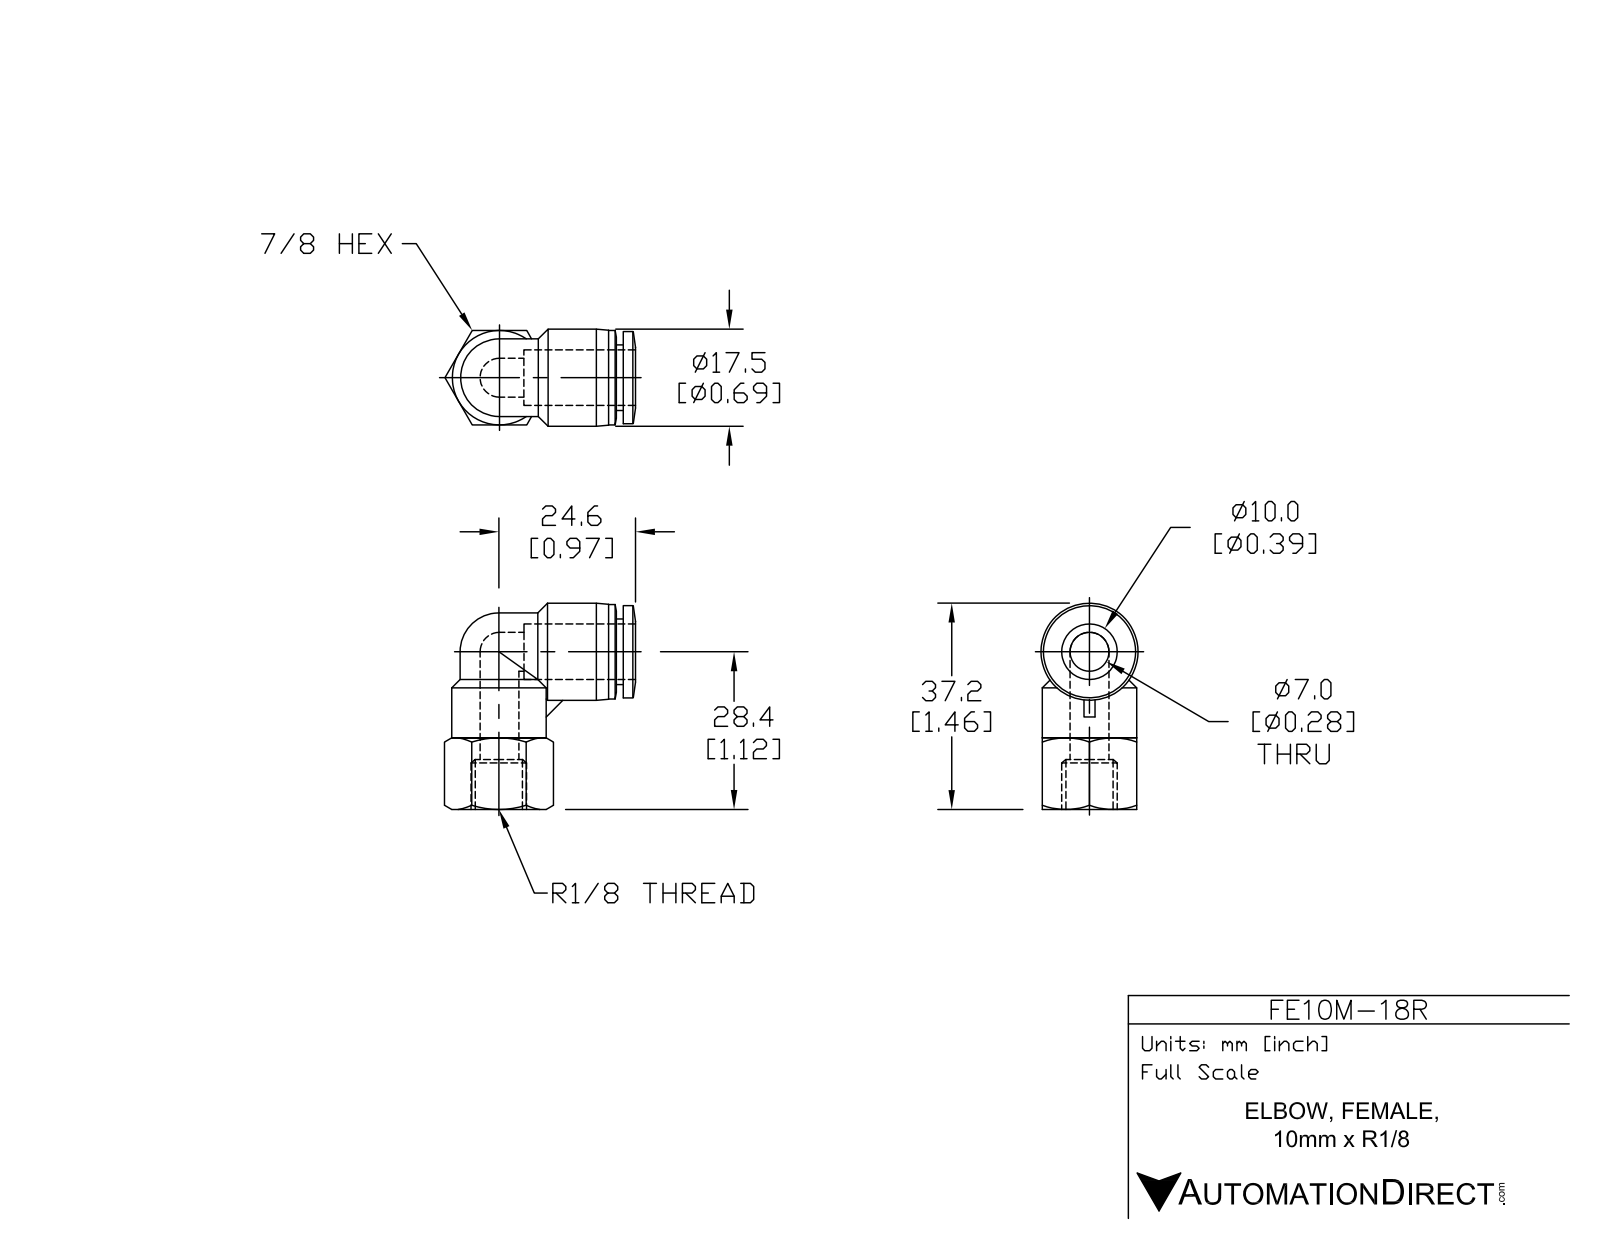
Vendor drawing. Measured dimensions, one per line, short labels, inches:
name: FE10M-18R
written by: SolidWorks 2015 (AUTOMOTIVE_DESIGN)
unit: in
bodies: 1 solid, 69 faces (16 planar, 20 cylindrical, 33 other)
size: 1.467 × 1.355 × 0.689
volume: 0.486 in³; area: 7.407 in²
holes: 2× ⌀0.276, 1× ⌀0.406
bosses: 2× ⌀0.669, 1× ⌀0.689, 1× ⌀0.654, 1× ⌀0.551, 1× ⌀0.465
rounds: 1× R0.276
face distances: 0.669, 0.049, 0.659, 0.709, 0.354, 0.295, 0.374, 0.079, 0.604, 0.055
